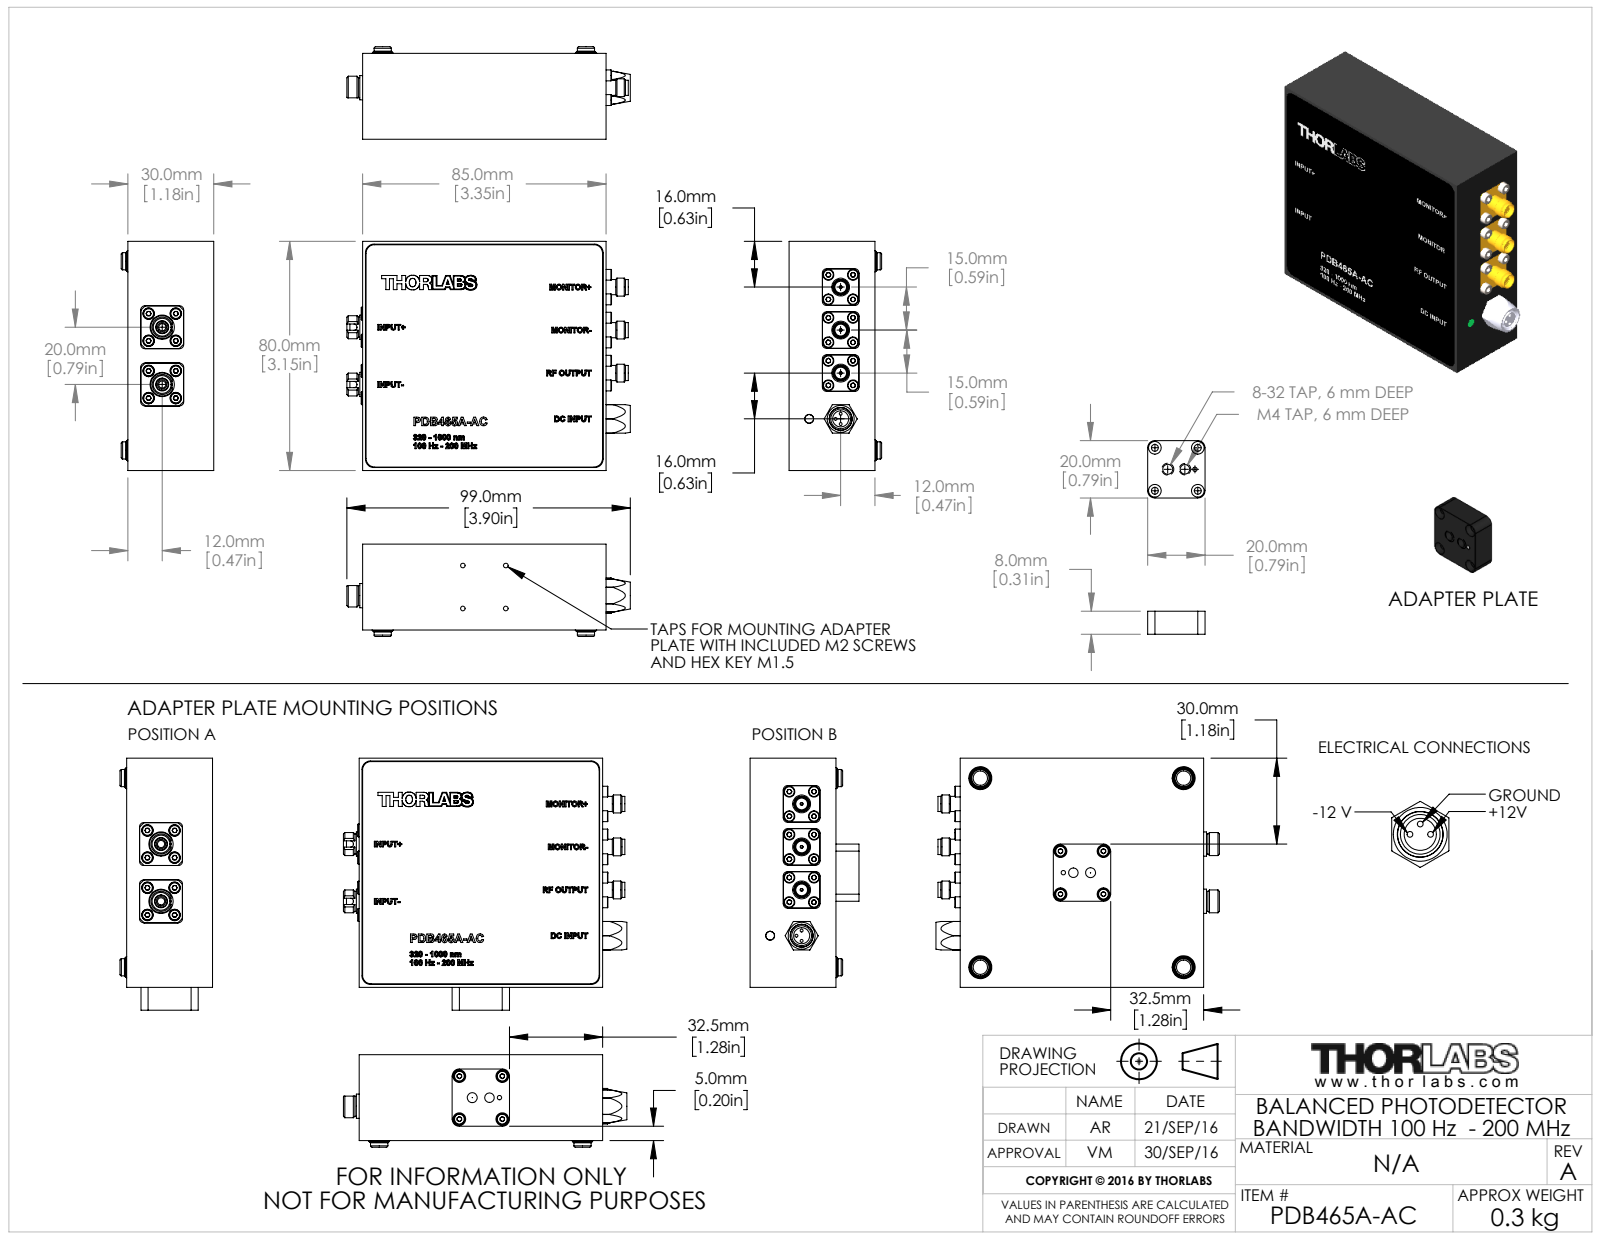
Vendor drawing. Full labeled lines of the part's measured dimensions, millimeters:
Part name (STEP PRODUCT): MTN005474-E0W
STEP written by: SolidWorks 2014 (AUTOMOTIVE_DESIGN)
Units: millimetres
Bodies: 90 solids, 3104 faces (1795 planar, 584 cylindrical, 725 other)
Overall size (bounding box): 99 × 88 × 38
Volume: 87 719 mm³ · Surface area: 57 809 mm²
Round holes (diameter × count): ⌀1.6 ×38, ⌀2.6 ×12, ⌀2.2 ×8, ⌀2.4 ×8, ⌀4 ×8, ⌀4.4 ×8, ⌀1.02 ×6, ⌀8 ×5, ⌀0.8 ×3, ⌀1 ×3, ⌀4.1 ×3, ⌀4.2 ×3
Round bosses / shafts (diameter × count): ⌀3.8 ×20, ⌀2 ×20, ⌀4.5 ×8, ⌀2.5 ×8, ⌀0.43 ×6, ⌀6 ×4, ⌀6.22 ×3, ⌀5.3 ×3
Partial cylindrical surfaces — rounded edges, fillets, slot ends (radius × count): R1.5 ×20, R3 ×12, R2.5 ×8, R5 ×8, R1 ×4, R9.5 ×2, R5.75 ×1
Main face-to-face distances: 29.7, 6, 23.7, 5.5, 80, 2, 74.5, 85, 3.5, 83
Hole centre spacings: 15, 6.08, 8.6, 9.5, 6.72, 8.75, 11.53, 12.9
